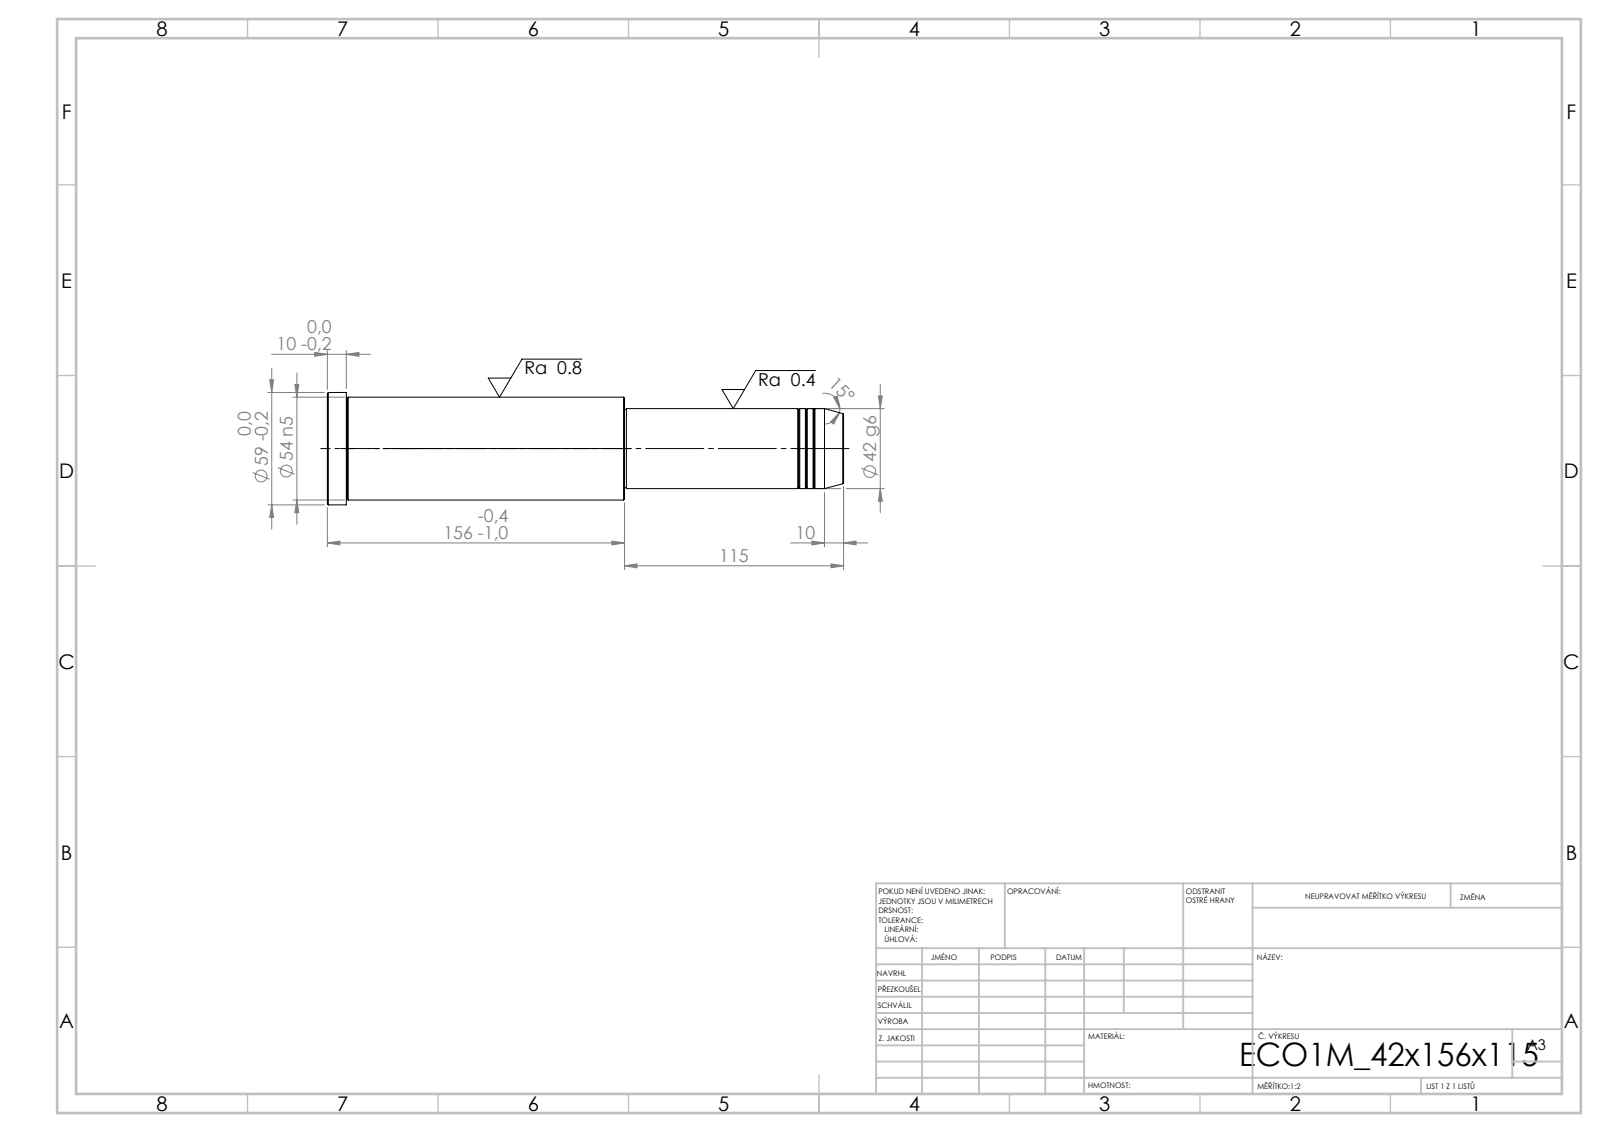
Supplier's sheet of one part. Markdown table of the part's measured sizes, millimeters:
| quantity | value |
| --- | --- |
| STEP written by | SolidWorks 2019 (CONFIG_CONTROL_DESIGN) |
| units | millimeters |
| bodies | 1 solid, 43 faces (5 planar, 14 cylindrical, 24 other) |
| overall size | 271 × 59 × 59 |
| volume | 519 013 mm³ |
| surface area | 47 212 mm² |
| round bosses / shafts (diameter × count) | 59 × 1, 54 × 1, 42 × 1, 41 × 1 |
| main face-to-face distances | 271, 115, 156, 261, 146, 10, 114, 1, 147, 157 |
